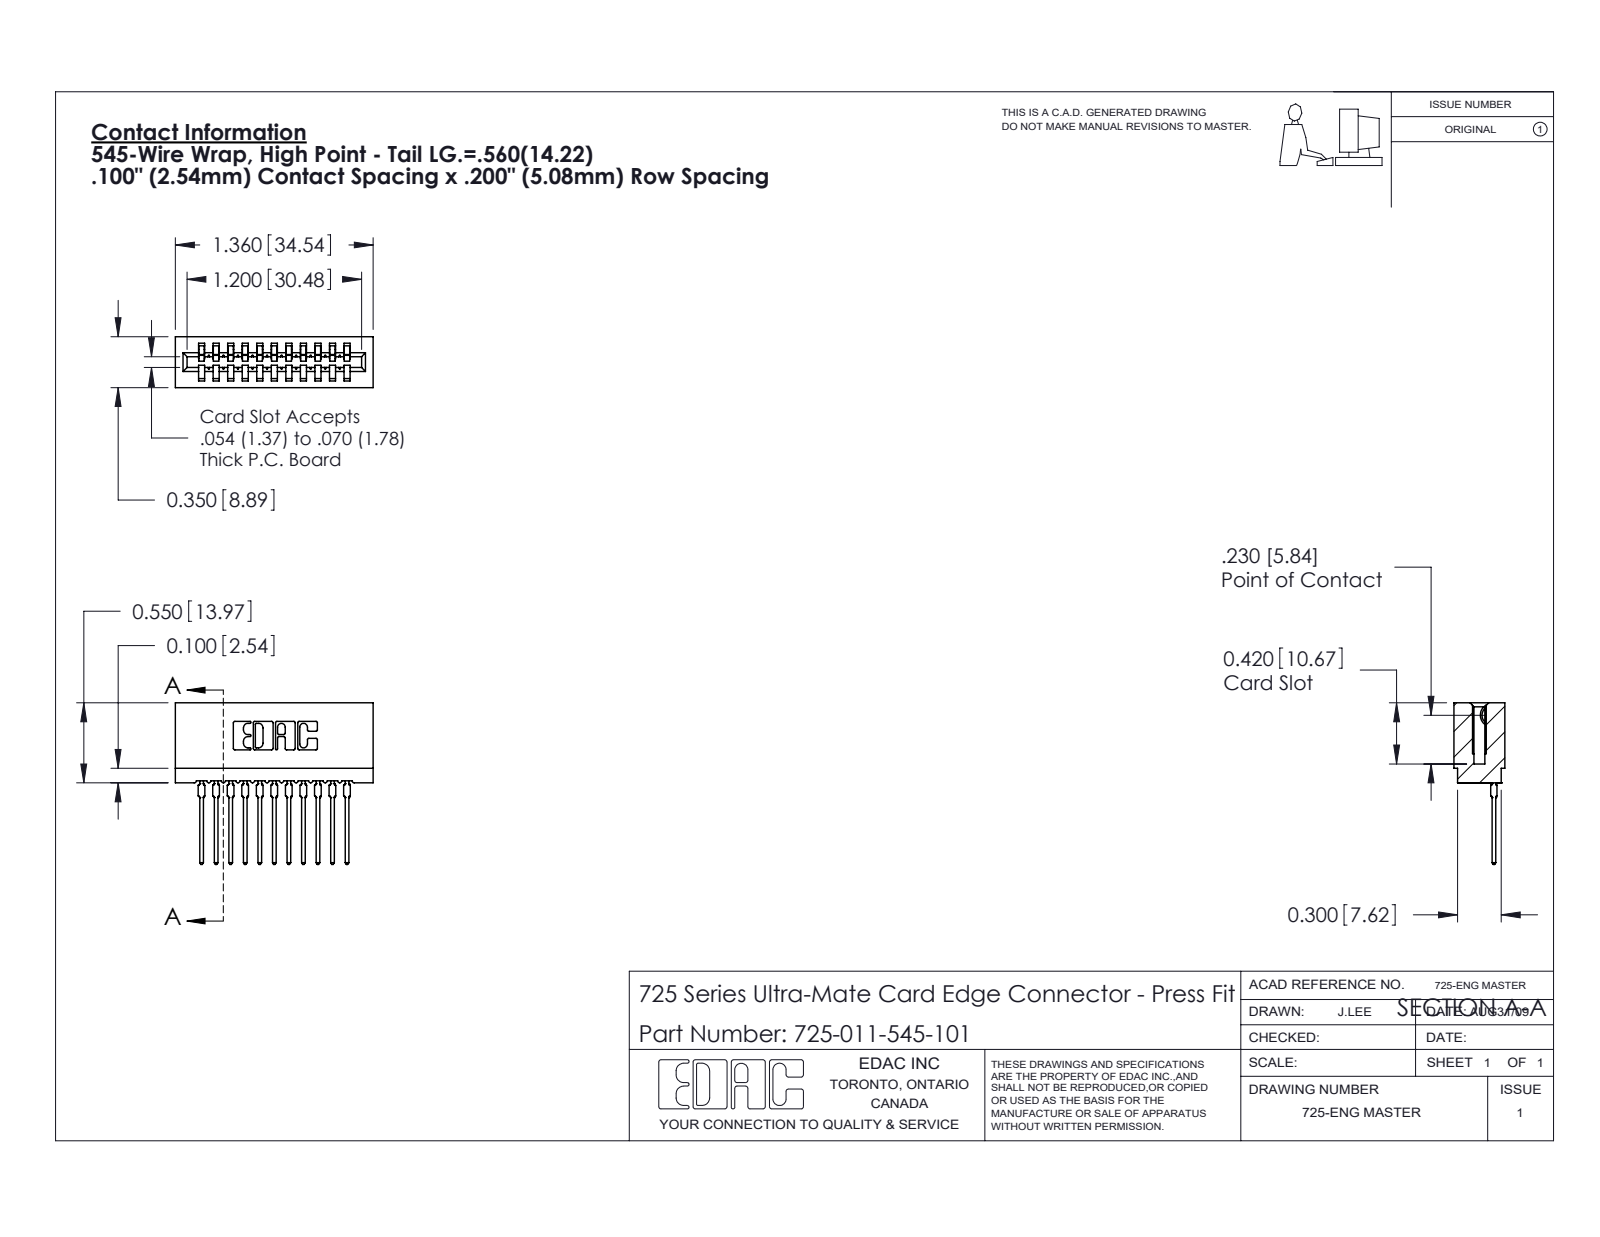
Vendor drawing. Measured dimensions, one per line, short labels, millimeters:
name: 725 Part_Insulator Option - 01; 745-292-001_545; 725-011-545-101
written by: SolidWorks 2020 (CONFIG_CONTROL_DESIGN)
unit: mm
bodies: 12 solids, 1327 faces (792 planar, 249 cylindrical, 286 other)
size: 34.5 × 28.2 × 8.9
volume: 2 820 mm³; area: 5 040 mm²
rounds: 22× R0.3, 22× R0.4, 22× R0.5, 6× R0.2, 6× R0.8, 4× R0.1, 4× R0.3, 3× R0.7
face distances: 2.5, 5.1, 7.6, 10.2, 12.7, 4, 1.5, 1.1, 3.6, 6.6
